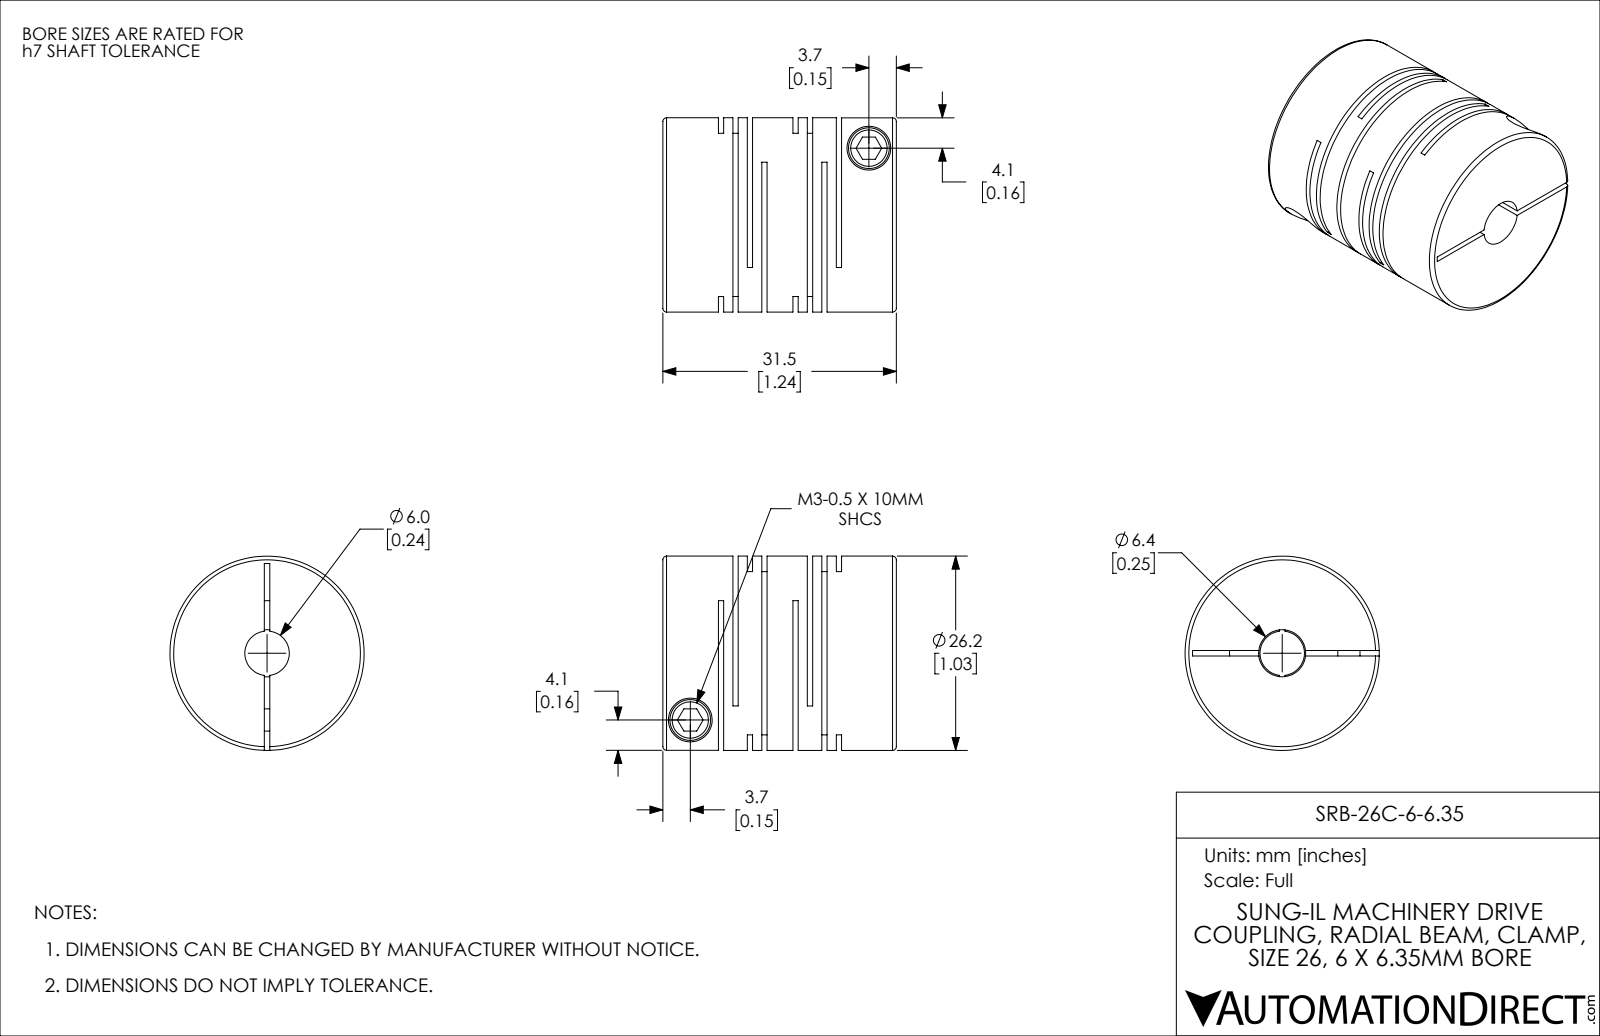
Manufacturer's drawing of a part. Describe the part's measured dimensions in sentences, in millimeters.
The part is named "SRB-26C-6-6". Its 3-D file was written by "SolidWorks 2021 (CONFIG_CONTROL_DESIGN)". It is 1 solid with 114 faces: 60 planar, 42 cylindrical and 12 other. Overall it measures 31.5 by 26.2 by 26.2 millimeters. Its volume is 13 196 cubic millimeters and its surface area 11 413 square millimeters. Round holes: 2 of diameter 3, 2 of diameter 5.9, 1 of diameter 6. Round bosses or shafts: 2 of diameter 5.5, 1 of diameter 26.2. The main face-to-face distances are 1.95, 10.05, 0.71, 3.9, 8.1, 12, 1.24, 2.66, 9.34, 13.95.
